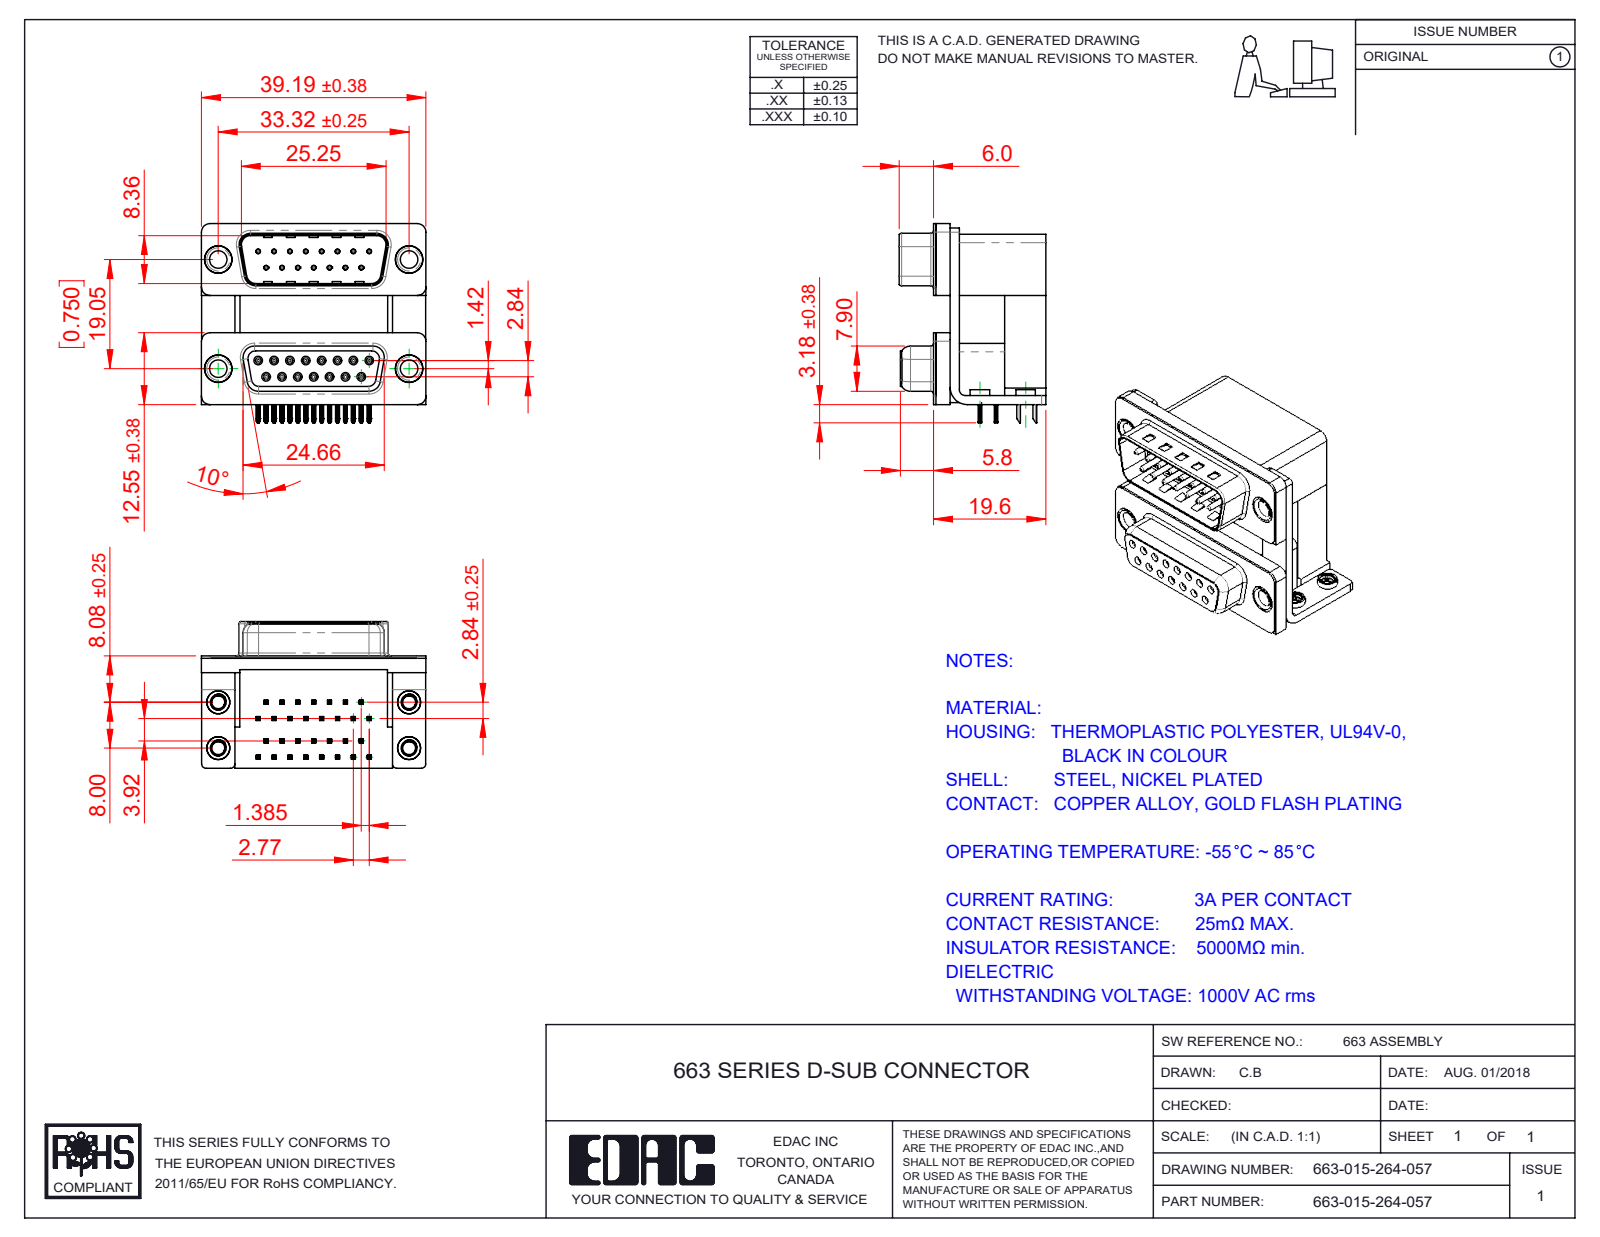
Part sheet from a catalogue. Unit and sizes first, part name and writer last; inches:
Units: inches
Overall size (bounding box): 1.543 × 1.369 × 1.008
Round holes (diameter × count): ⌀0.031 ×30, ⌀0.014 ×15, ⌀0.035 ×15, ⌀0.089 ×4, ⌀0.108 ×4, ⌀0.12 ×4, ⌀0.126 ×4, ⌀0.138 ×4, ⌀0.157 ×4, ⌀0.189 ×4, ⌀0.197 ×4
Round bosses / shafts (diameter × count): ⌀0.047 ×15, ⌀0.03 ×15, ⌀0.193 ×4, ⌀0.187 ×4, ⌀0.157 ×4, ⌀0.152 ×4, ⌀0.134 ×4
Partial cylindrical surfaces — rounded edges, fillets, slot ends (radius × count): R0.004 ×120, R0.006 ×60, R0.01 ×60, R0.005 ×30, R0.014 ×30, R0.059 ×16, R0.013 ×15, R0.02 ×12
Main face-to-face distances: 0.016, 0.756, 0.657, 0.098, 0.283, 0.472, 0.374, 0.421, 0.114, 0.063
Hole centre spacings: 0.124, 0.758, 0.109, 0.781, 0.218, 0.327, 0.75, 0.818
Volume: 0.93 in³ · Surface area: 26.28 in²
Bodies: 45 solids, 3968 faces (2027 planar, 1054 cylindrical, 887 other)
Part name (STEP PRODUCT): 663-015-264-057; 663 Contact Top Upper_M; 663 Housing Lower_15 Contacts; 663 Mounting Bracket_ThruM (+8 more)
STEP written by: SolidWorks 2020 (CONFIG_CONTROL_DESIGN)
